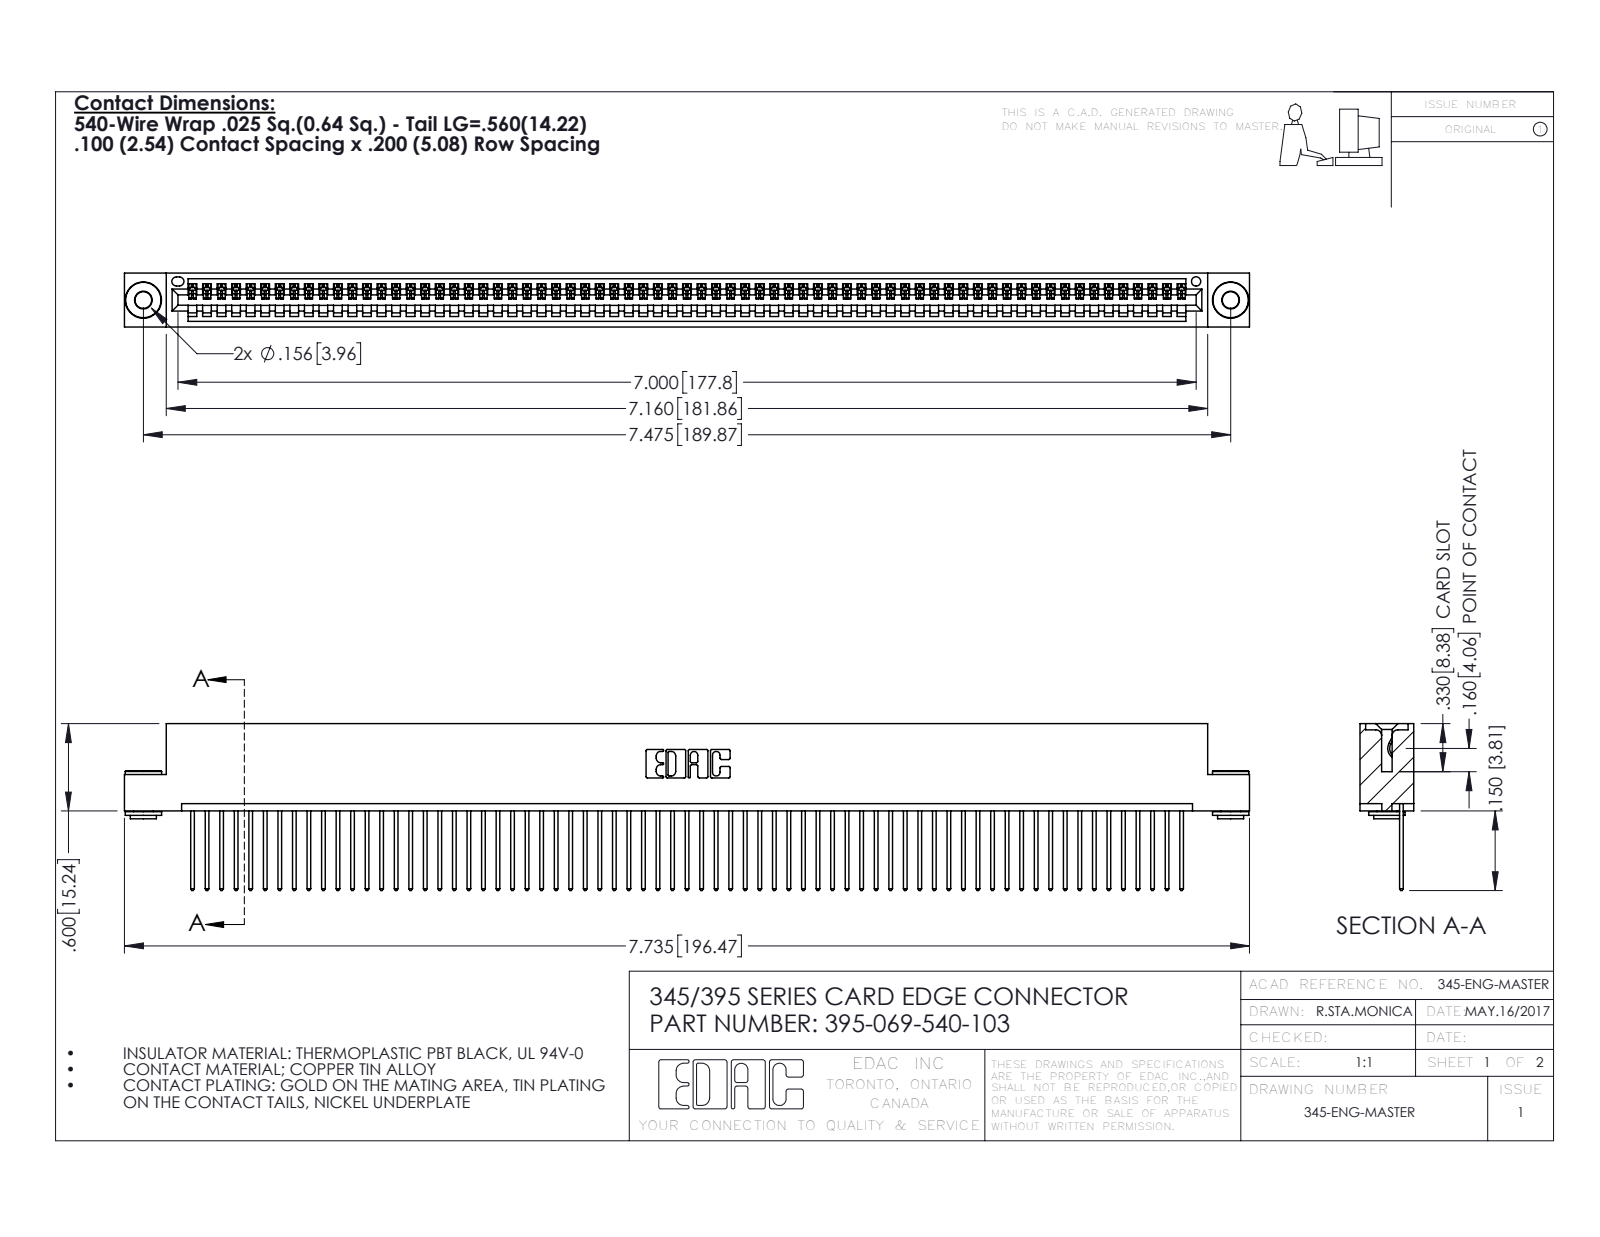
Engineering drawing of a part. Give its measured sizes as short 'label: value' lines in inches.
name: 345 Part_Flush Mounting Lugs - 0.156 Dia-TH; 345-292-001_345-293-140; 345-250-002_345-250-002-102; 395-069-540-103
written by: SolidWorks 2016 (CONFIG_CONTROL_DESIGN)
unit: in
bodies: 72 solids, 4166 faces (2850 planar, 1308 cylindrical, 8 other)
size: 7.735 × 1.147 × 0.37
volume: 1.159 in³; area: 41.07 in²
holes: 2× ⌀0.116, 2× ⌀0.156, 1× ⌀0.064
bosses: 2× ⌀0.25, 2× ⌀0.18, 2× ⌀0.136
rounds: 138× R0.006, 138× R0.01, 22× R0.01, 6× R0.007, 6× R0.031, 3× R0.026, 2× R0.031, 2× R0.04
face distances: 0.072, 0.298, 0.37, 0.025, 0.098, 0.272, 0.2, 0.225, 0.149, 0.072
hole spacings: 0.27, 7.239, 7.475
